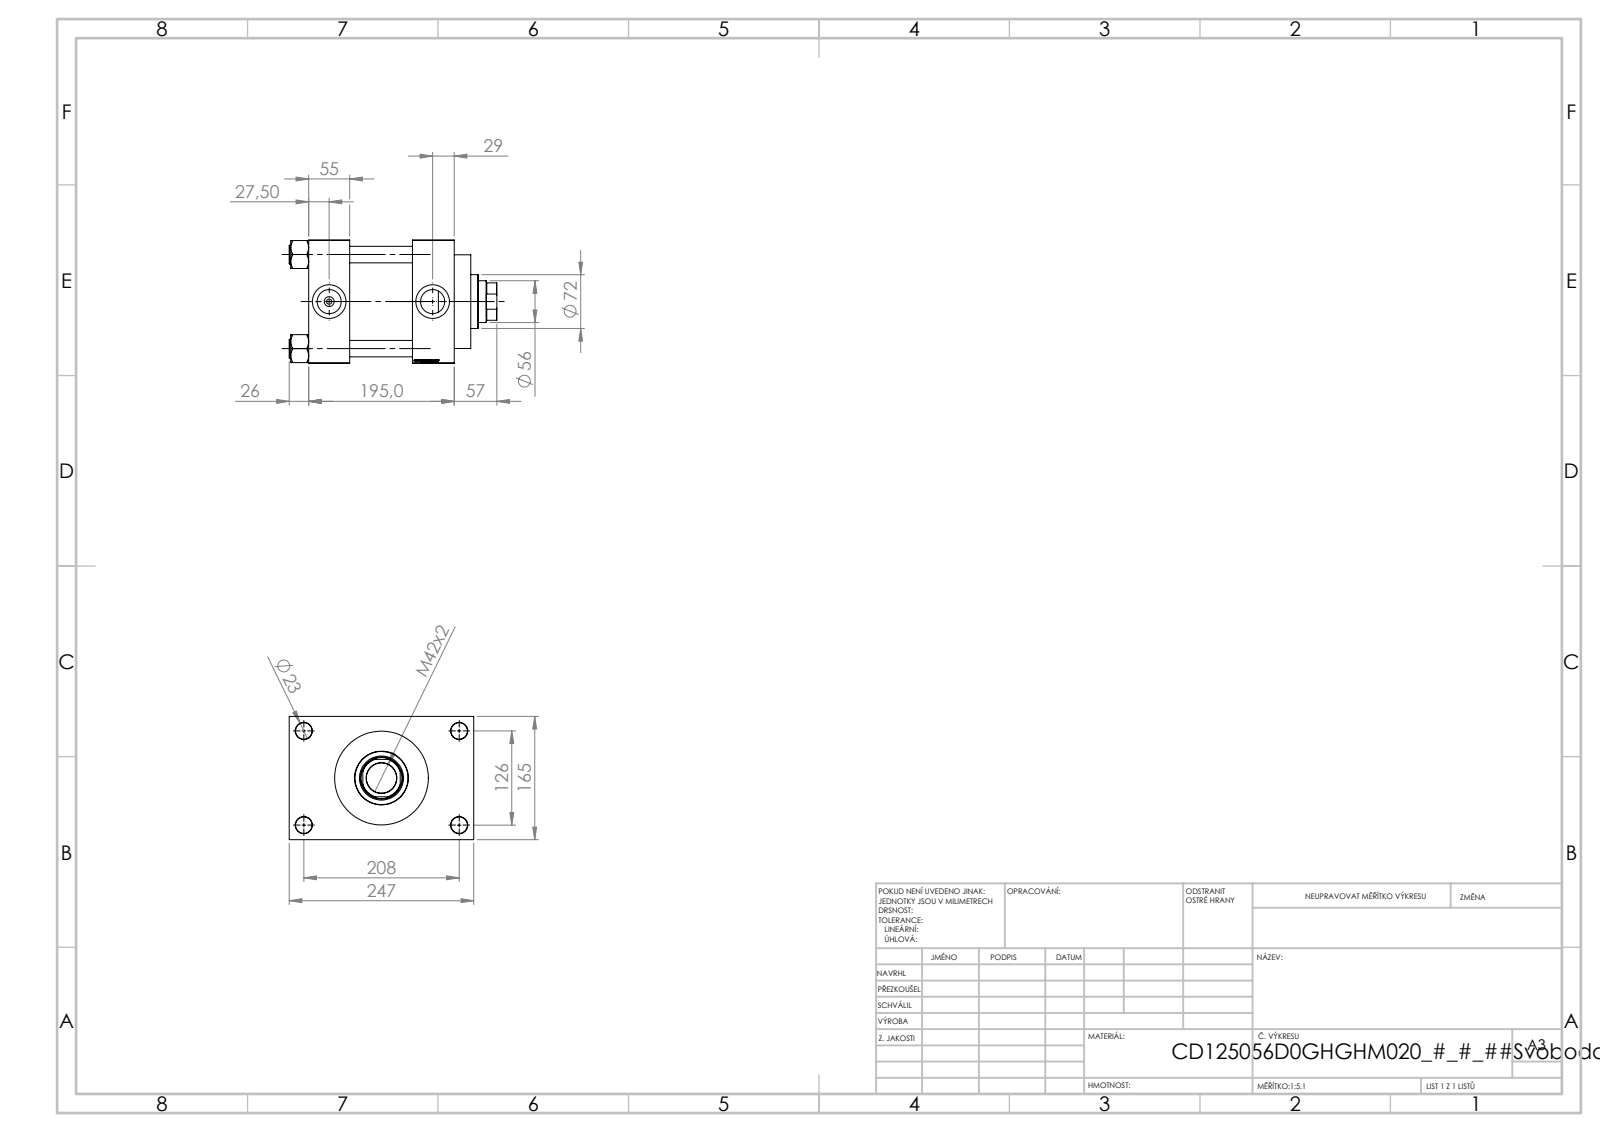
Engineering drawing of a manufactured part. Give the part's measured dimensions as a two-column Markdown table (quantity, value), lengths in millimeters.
| quantity | value |
| --- | --- |
| part name | V215CD_D_TYCINKA; V215CD_D_Body; V215CD_VC_A; V215CD_NUT_M5_D (+1 more) |
| STEP written by | SolidWorks 2019 (CONFIG_CONTROL_DESIGN) |
| units | millimeters |
| bodies | 11 solids, 1148 faces (544 planar, 86 cylindrical, 518 other) |
| overall size | 278 × 247 × 165 |
| volume | 4 924 000 mm³ |
| surface area | 534 057 mm² |
| round holes (diameter × count) | 22 × 8, 7 × 2, 32.24 × 2, 45 × 2, 40.5 × 1, 56 × 1, 59 × 1, 96 × 1, 125 × 1, 125.5 × 1 |
| round bosses / shafts (diameter × count) | 25 × 4, 131 × 1, 72 × 1 |
| partial cylindrical surfaces (radius × count) | 27 × 1 |
| main face-to-face distances | 165, 84, 55, 139, 56, 195, 140, 41, 206, 173.74 |
| hole center spacings | 41.05, 89.02, 121.59, 125.9, 132.47, 166.95, 209.13, 126 |
